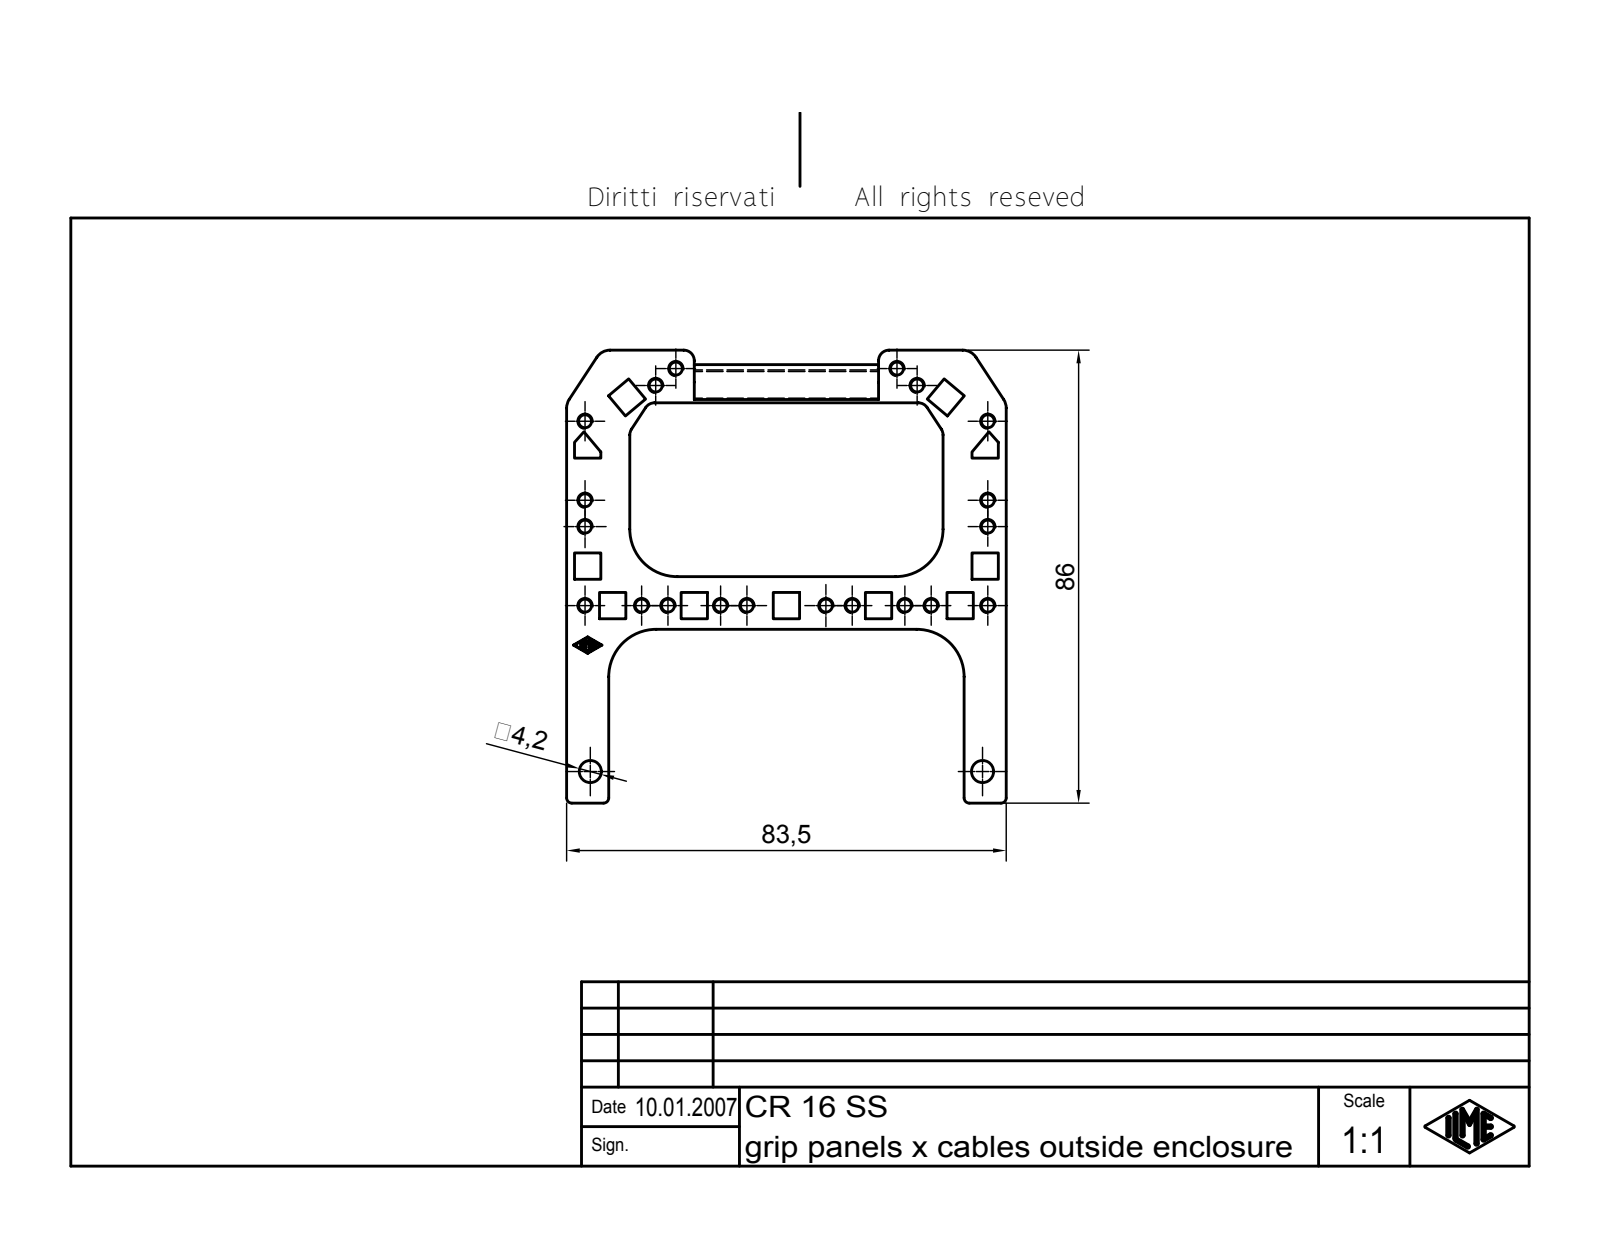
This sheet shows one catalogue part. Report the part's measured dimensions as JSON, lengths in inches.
{"part_name": "CR 16 SS", "step_written_by": "Autodesk Inventor 7 (AUTOMOTIVE_DESIGN)", "units": "inches", "bodies": {"solids": 1, "faces": 203, "planar": 117, "cylindrical": 46, "other": 40}, "overall_size": [3.386, 3.287, 0.217], "volume_in3": 0.335, "surface_area_in2": 12.41, "round_holes": [[0.165, 2]], "partial_cylinders_radius": [[0.004, 14], [0.079, 6], [0.039, 4], [0.118, 4], [0.354, 4], [0.069, 1], [0.108, 1]], "face_to_face_distances": [0.079, 0.039, 1.693, 0.197, 3.287, 0.315, 0.394, 0.157, 1.299, 2.972], "hole_center_spacings": [2.933]}
